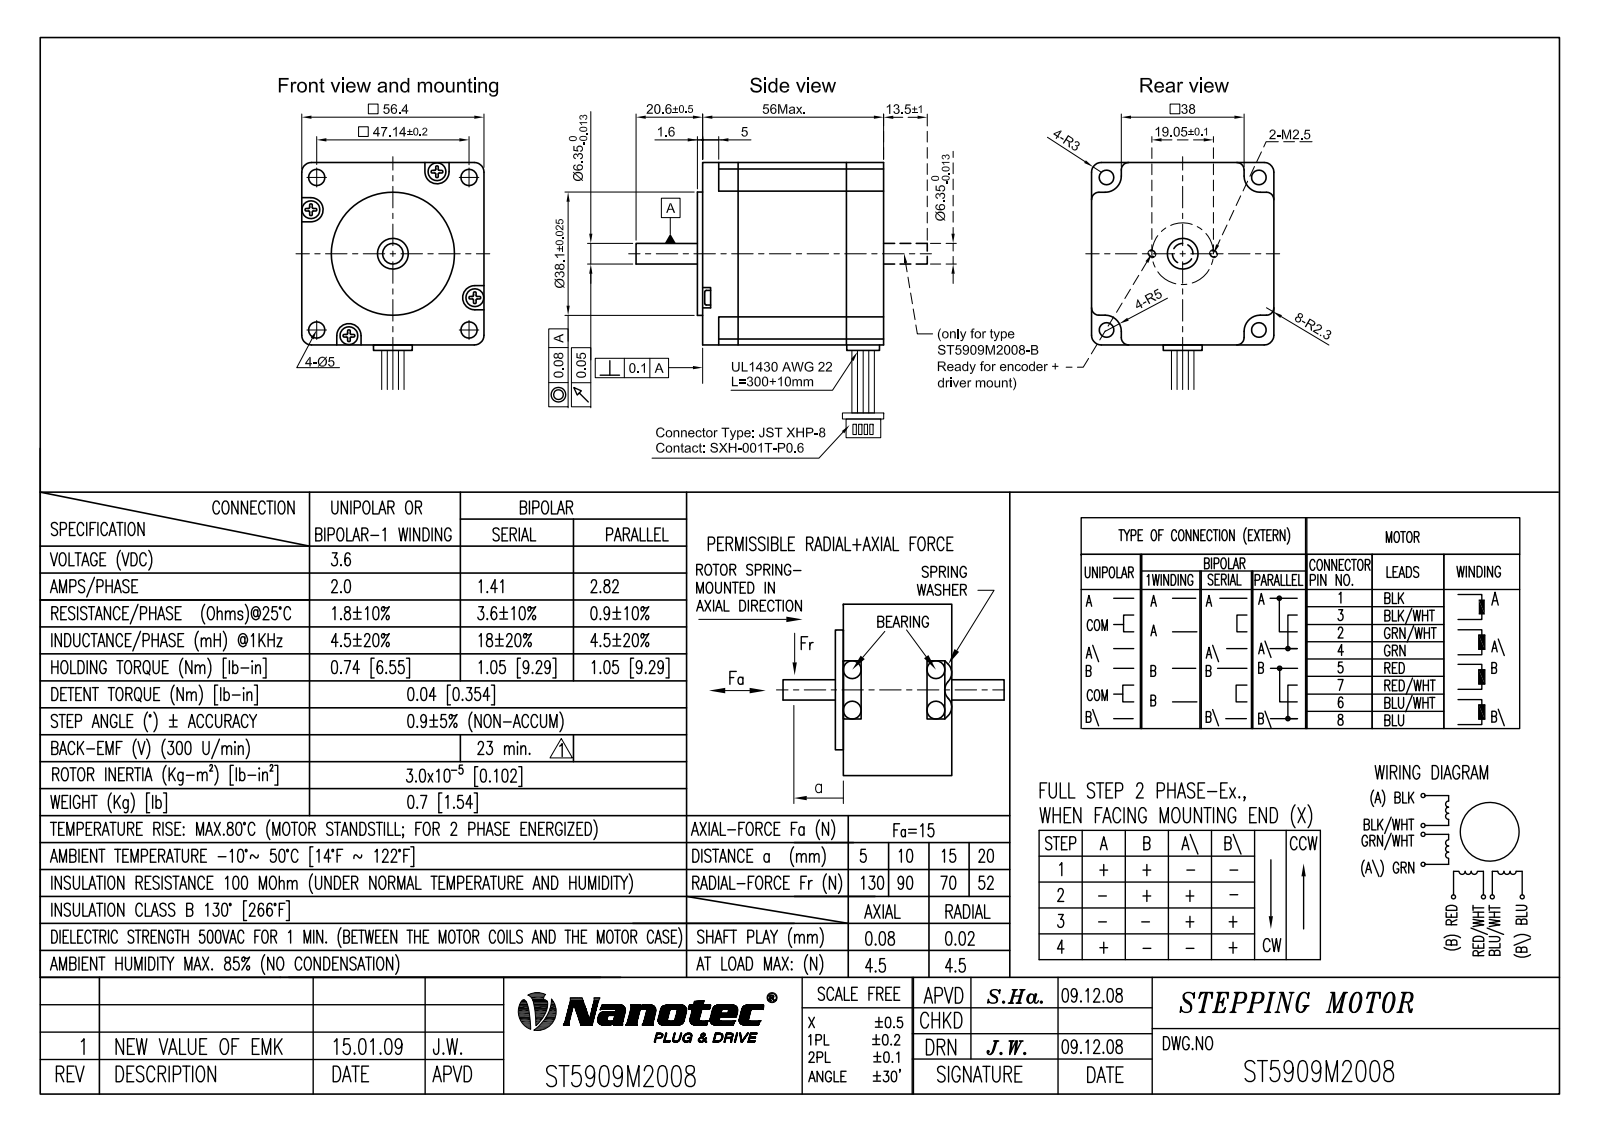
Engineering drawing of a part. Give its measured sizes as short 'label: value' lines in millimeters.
name: ST5909M
written by: Autodesk Inventor 2010 (AUTOMOTIVE_DESIGN)
unit: mm
bodies: 1 solid, 288 faces (211 planar, 73 cylindrical, 4 other)
size: 88.1 × 73.1 × 56.4
volume: 162 227 mm³; area: 19 950 mm²
holes: 4× ⌀3, 4× ⌀5, 1× ⌀2.01, 1× ⌀2.01
bosses: 8× ⌀1, 4× ⌀5.5, 1× ⌀38.1, 1× ⌀6.35
rounds: 16× R2.3, 4× R3, 4× R3.75, 4× R5
face distances: 56.4, 56, 57.6, 1.6, 62, 9.2, 47.2, 51, 5, 6.6
hole spacings: 12.5, 34.82, 39.19, 40.63, 47.14, 50.46, 60.02, 27.43
